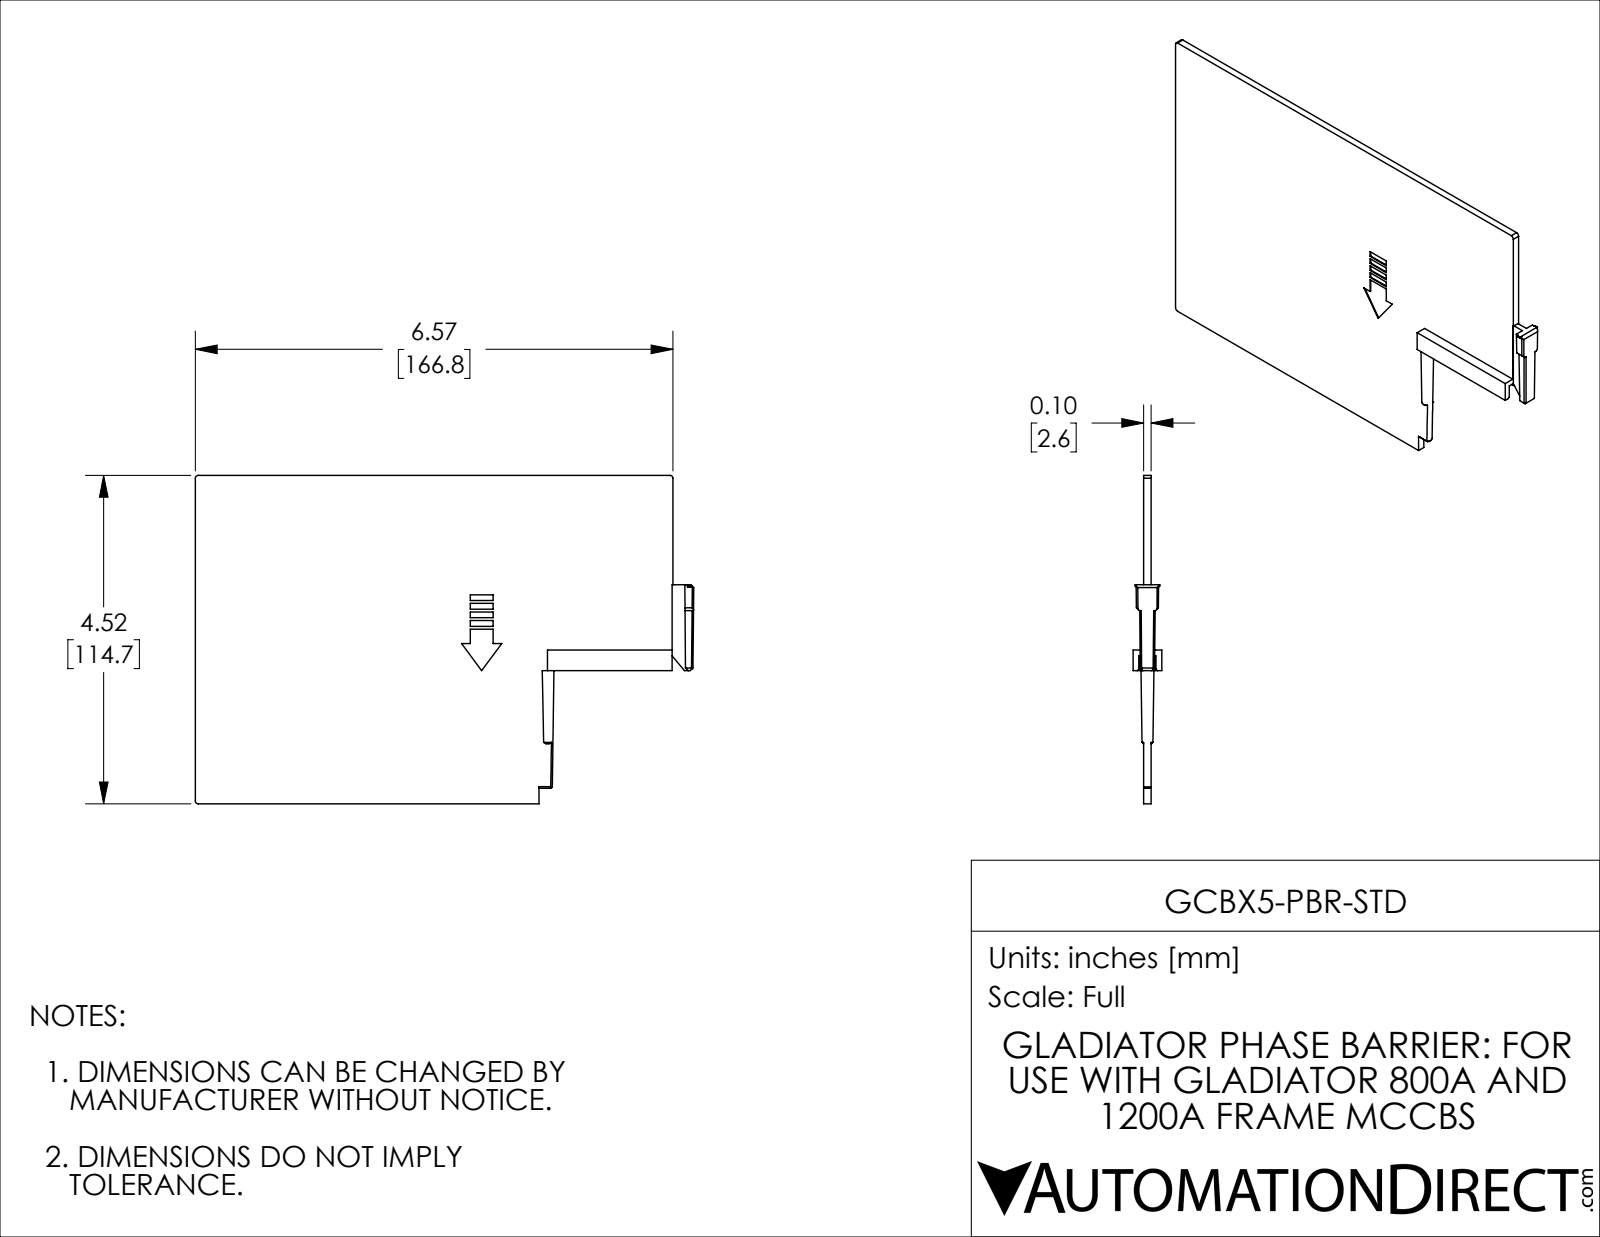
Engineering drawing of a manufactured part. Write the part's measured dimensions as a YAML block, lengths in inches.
part_name: "GCBX5-PBR-STD"
step_written_by: "SolidWorks 2021 (CONFIG_CONTROL_DESIGN)"
units: inches
bodies: {solids: 1, faces: 135, planar: 125, cylindrical: 3, other: 7}
overall_size: [6.853, 4.516, 0.394]
volume: 2.827
surface_area: 58.41
partial_cylinders:
  - {radius: 0.039, count: 3}
face_to_face_distances: [0.102, 0.079, 0.157, 0.236, 0.248, 0.146, 0.091, 0.315, 0.169, 0.067]
